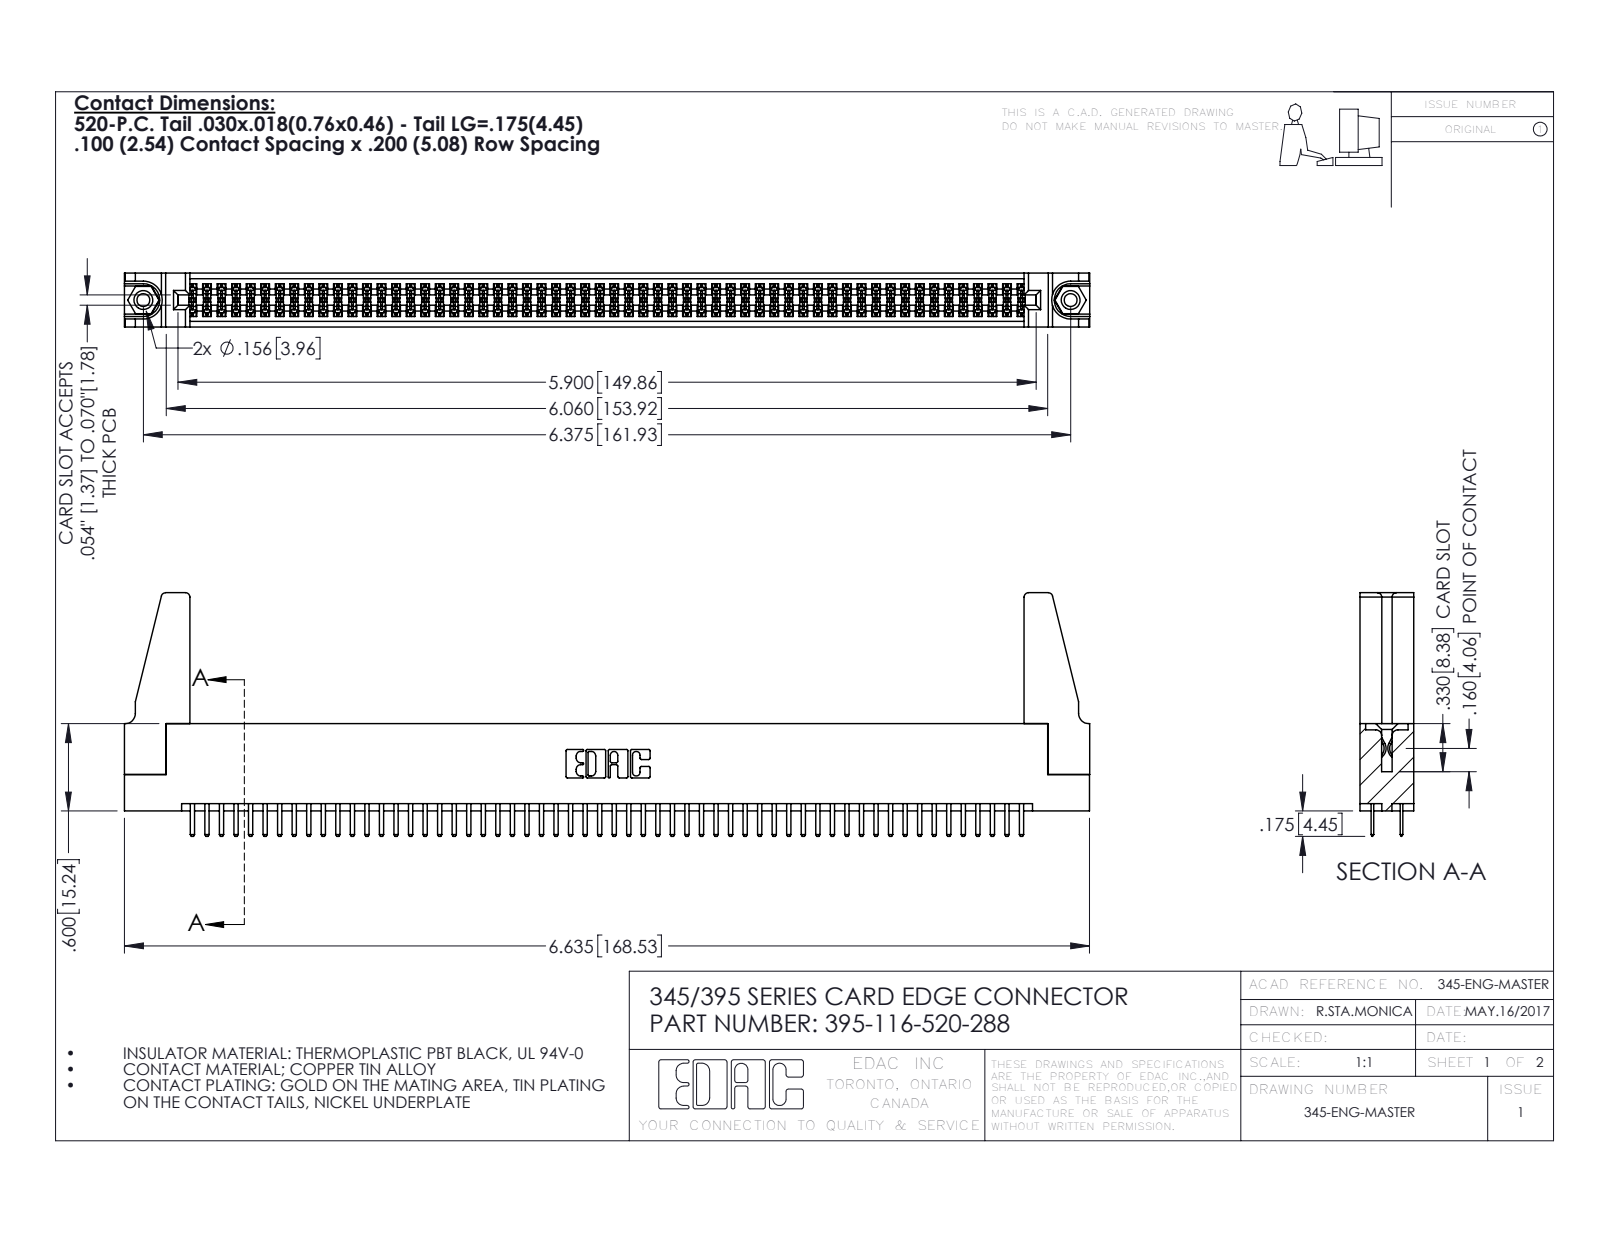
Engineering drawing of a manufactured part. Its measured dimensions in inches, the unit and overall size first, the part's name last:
Units: inches
Overall size (bounding box): 6.636 × 1.675 × 0.37
Round holes (diameter × count): ⌀0.089 ×2, ⌀0.125 ×2, ⌀0.156 ×2, ⌀0.064 ×1
Round bosses / shafts (diameter × count): ⌀0.155 ×2
Partial cylindrical surfaces — rounded edges, fillets, slot ends (radius × count): R0.006 ×174, R0.01 ×120, R0.01 ×22, R0.03 ×8, R0.007 ×6, R0.031 ×6, R0.026 ×3, R0.014 ×2
Main face-to-face distances: 0.072, 0.298, 0.37, 0.2, 0.098, 0.272, 0.025, 0.225, 0.022, 0.072
Hole centre spacings: 0.27, 6.139, 6.375
Volume: 1.204 in³ · Surface area: 42.89 in²
Bodies: 121 solids, 6514 faces (4212 planar, 2286 cylindrical, 16 other)
Part name (STEP PRODUCT): 345-292-001_345-293-120; 345 Part_Flush Mounting Lugs - 0.156 Dia-TH; 345-250-001_345-250-001-102; 395-116-520-288 (+1 more)
STEP written by: SolidWorks 2016 (CONFIG_CONTROL_DESIGN)
